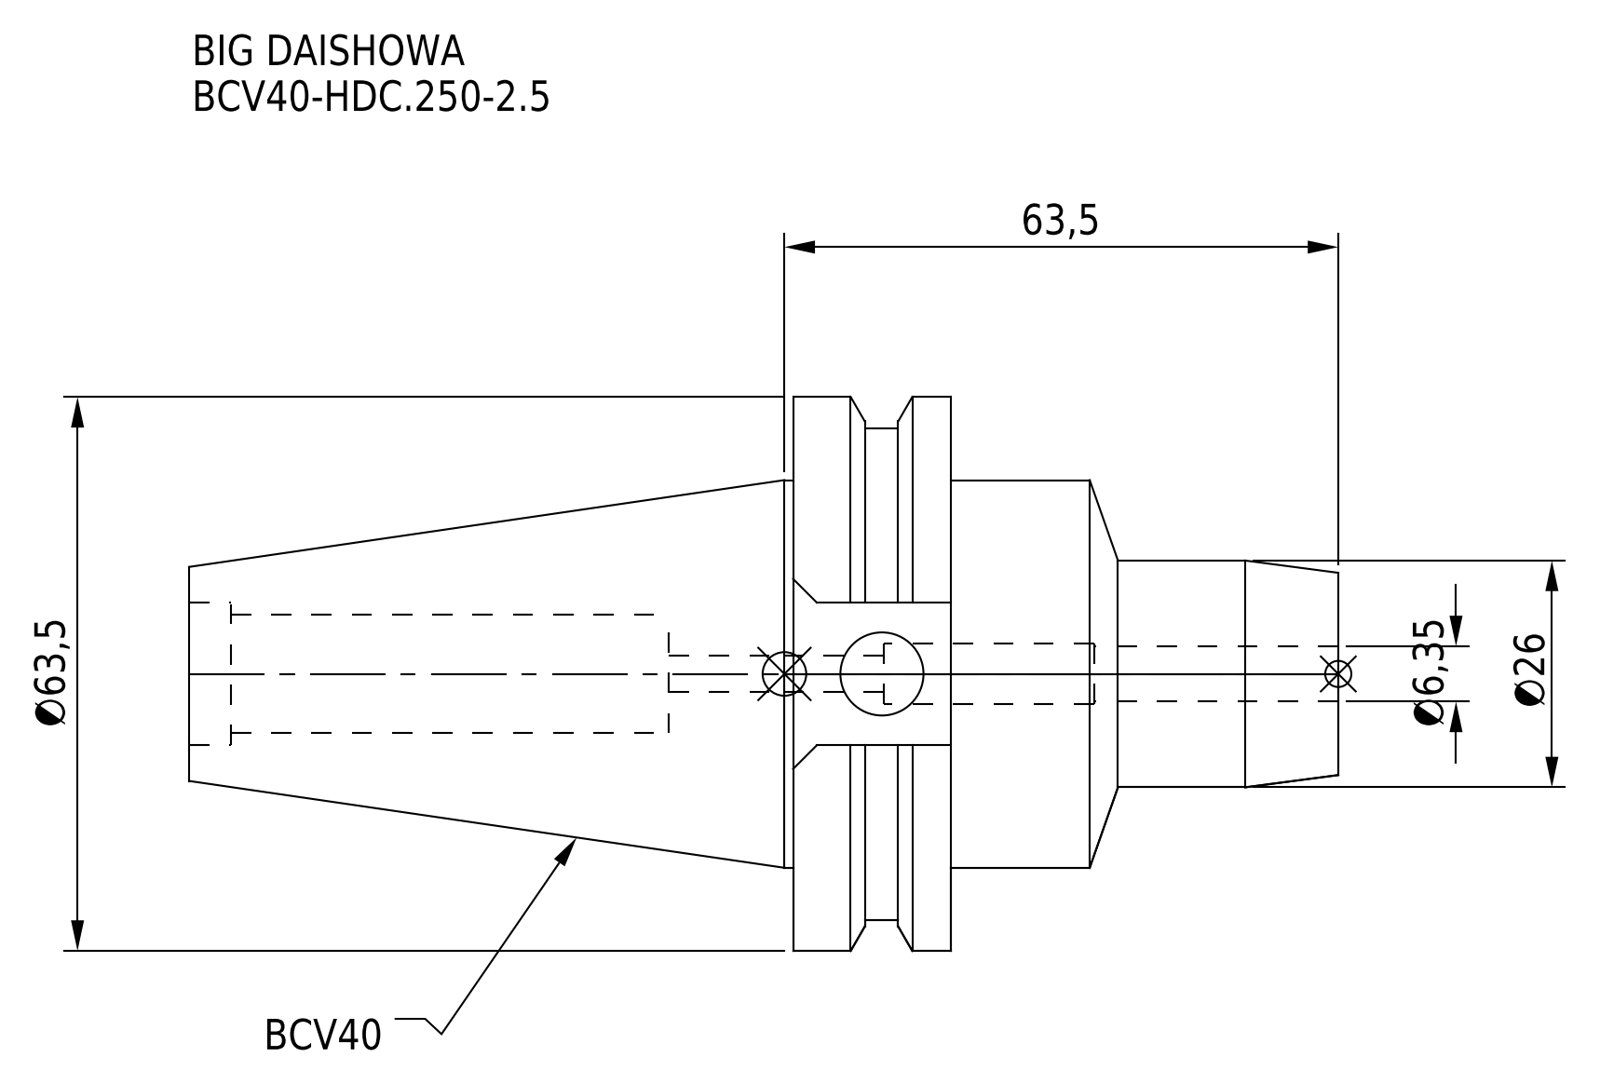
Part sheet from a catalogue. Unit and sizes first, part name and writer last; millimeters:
Units: millimetres
Overall size (bounding box): 131.75 × 63.5 × 61.35
Round holes (diameter × count): ⌀4.2 ×1, ⌀6.35 ×1, ⌀6.9 ×1, ⌀9.53 ×1, ⌀13.6 ×1, ⌀16.32 ×1
Round bosses / shafts (diameter × count): ⌀63.5 ×1, ⌀56.36 ×1, ⌀44.45 ×1, ⌀26 ×1
Main face-to-face distances: 18.05, 44.45, 62.5, 131.75, 87.3, 69.25, 47.55, 16.38, 76.75, 32.3
Volume: 147 179 mm³ · Surface area: 24 959 mm²
Bodies: 1 solid, 59 faces (23 planar, 26 cylindrical, 10 other)
Part name (STEP PRODUCT): BCV40-HDC_250-2_5
STEP written by: CREO PARAMETRIC BY PTC INC, 2016380 (AUTOMOTIVE_DESIGN)
